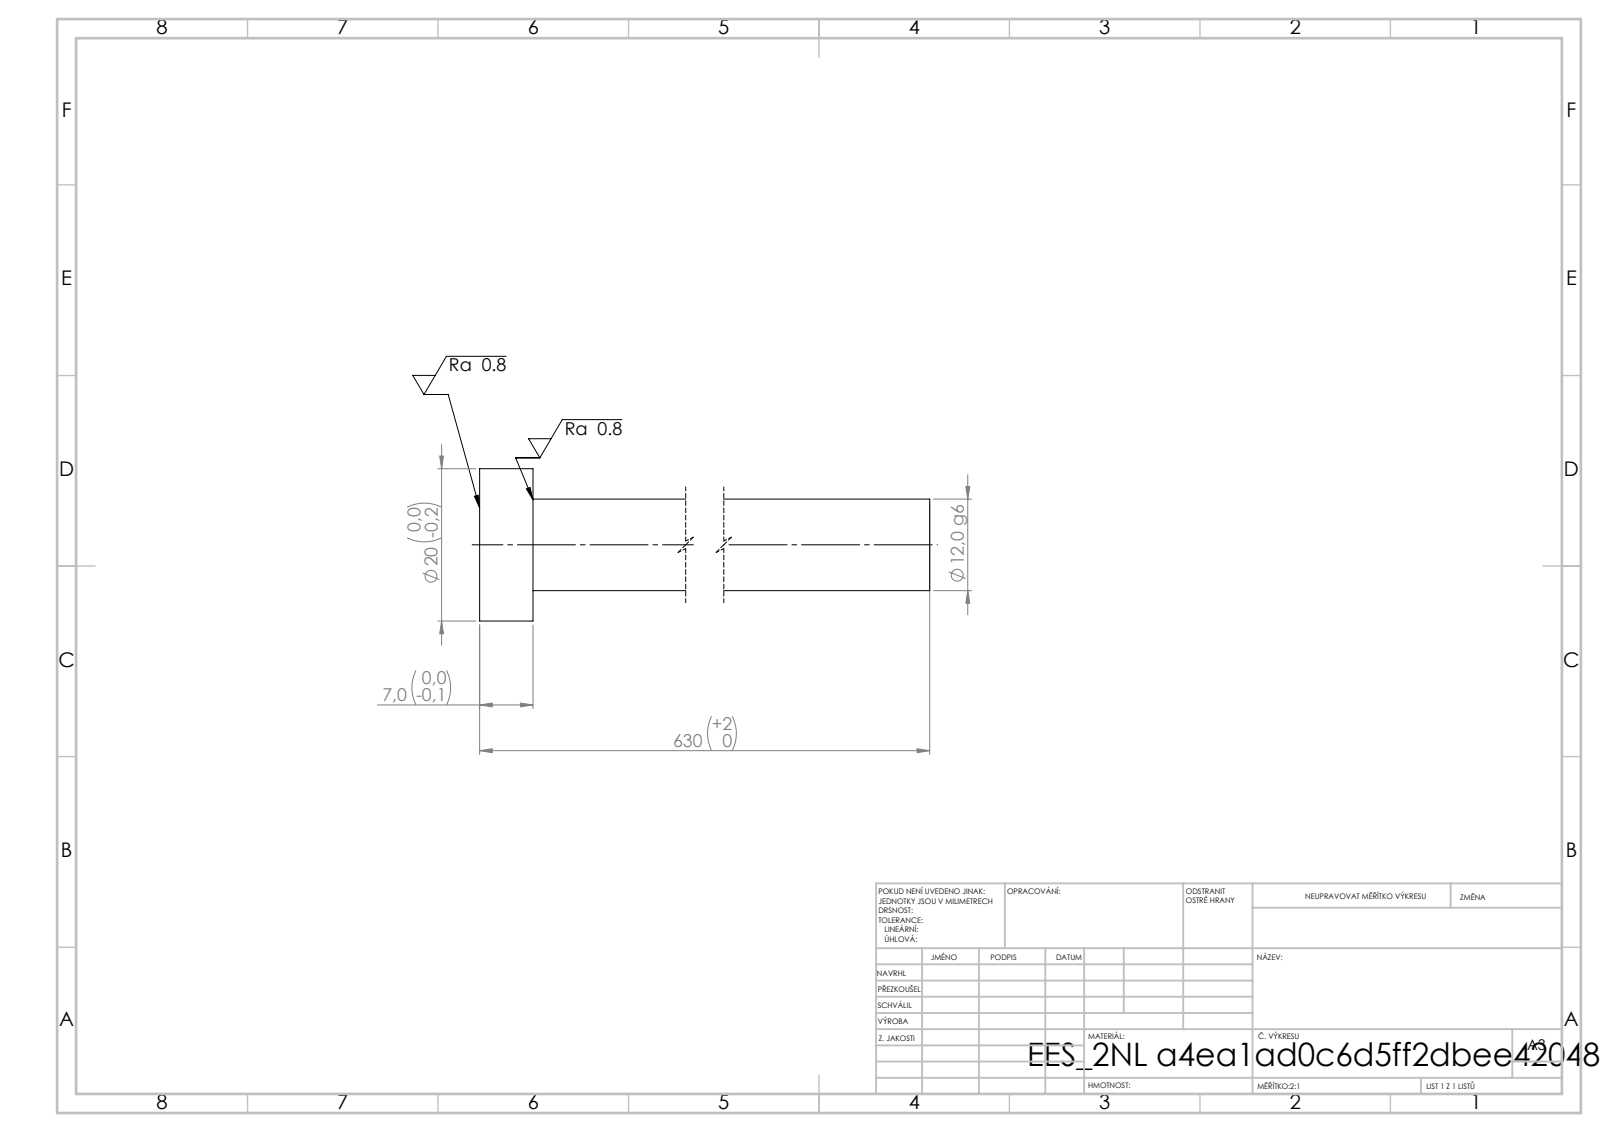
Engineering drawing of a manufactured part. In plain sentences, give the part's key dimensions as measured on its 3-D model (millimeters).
Its 3-D file was written by "SolidWorks 2019 (CONFIG_CONTROL_DESIGN)". It is 1 solid with 7 faces: 3 planar, 4 cylindrical and 0 other. Overall it measures 630 by 20 by 20 millimeters. Its volume is 72 659 cubic millimeters and its surface area 24 555 square millimeters. Round bosses or shafts: 1 of diameter 20, 1 of diameter 12. The main face-to-face distances are 7, 630, 623.
